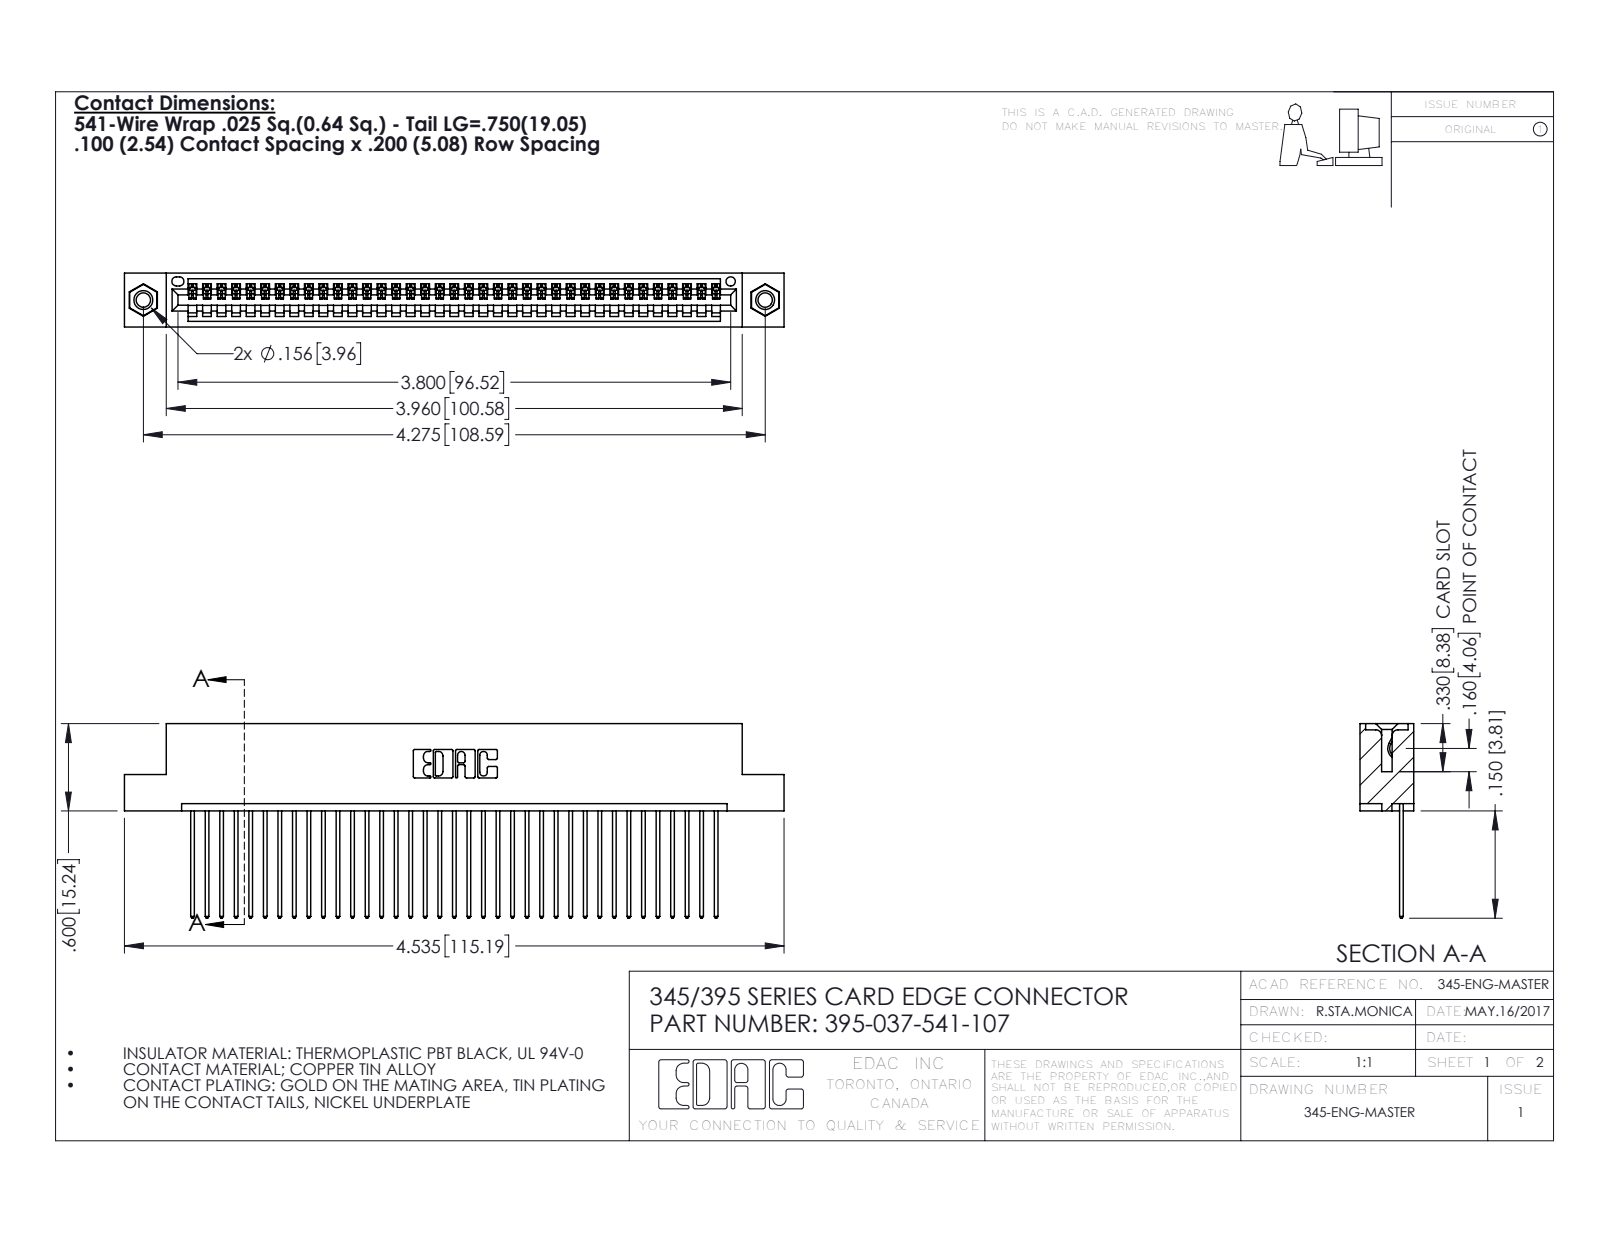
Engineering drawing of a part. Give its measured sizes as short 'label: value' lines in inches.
name: 395-037-541-107; 345-250-001_345-250-005-103; 345 Part_Flush Mounting Lugs - 0.156 Dia-TI; 345-292-001_345-293-141
written by: SolidWorks 2016 (CONFIG_CONTROL_DESIGN)
unit: in
bodies: 40 solids, 2332 faces (1592 planar, 724 cylindrical, 16 other)
size: 4.535 × 1.337 × 0.37
volume: 0.672 in³; area: 23.73 in²
holes: 2× ⌀0.098, 2× ⌀0.125, 2× ⌀0.156, 1× ⌀0.064
bosses: 2× ⌀0.155
rounds: 74× R0.006, 74× R0.01, 22× R0.01, 6× R0.007, 6× R0.031, 3× R0.026, 2× R0.031, 2× R0.04
face distances: 0.072, 0.298, 0.098, 0.272, 0.025, 0.2, 0.37, 0.225, 0.149, 0.072
hole spacings: 0.27, 4.039, 4.275
